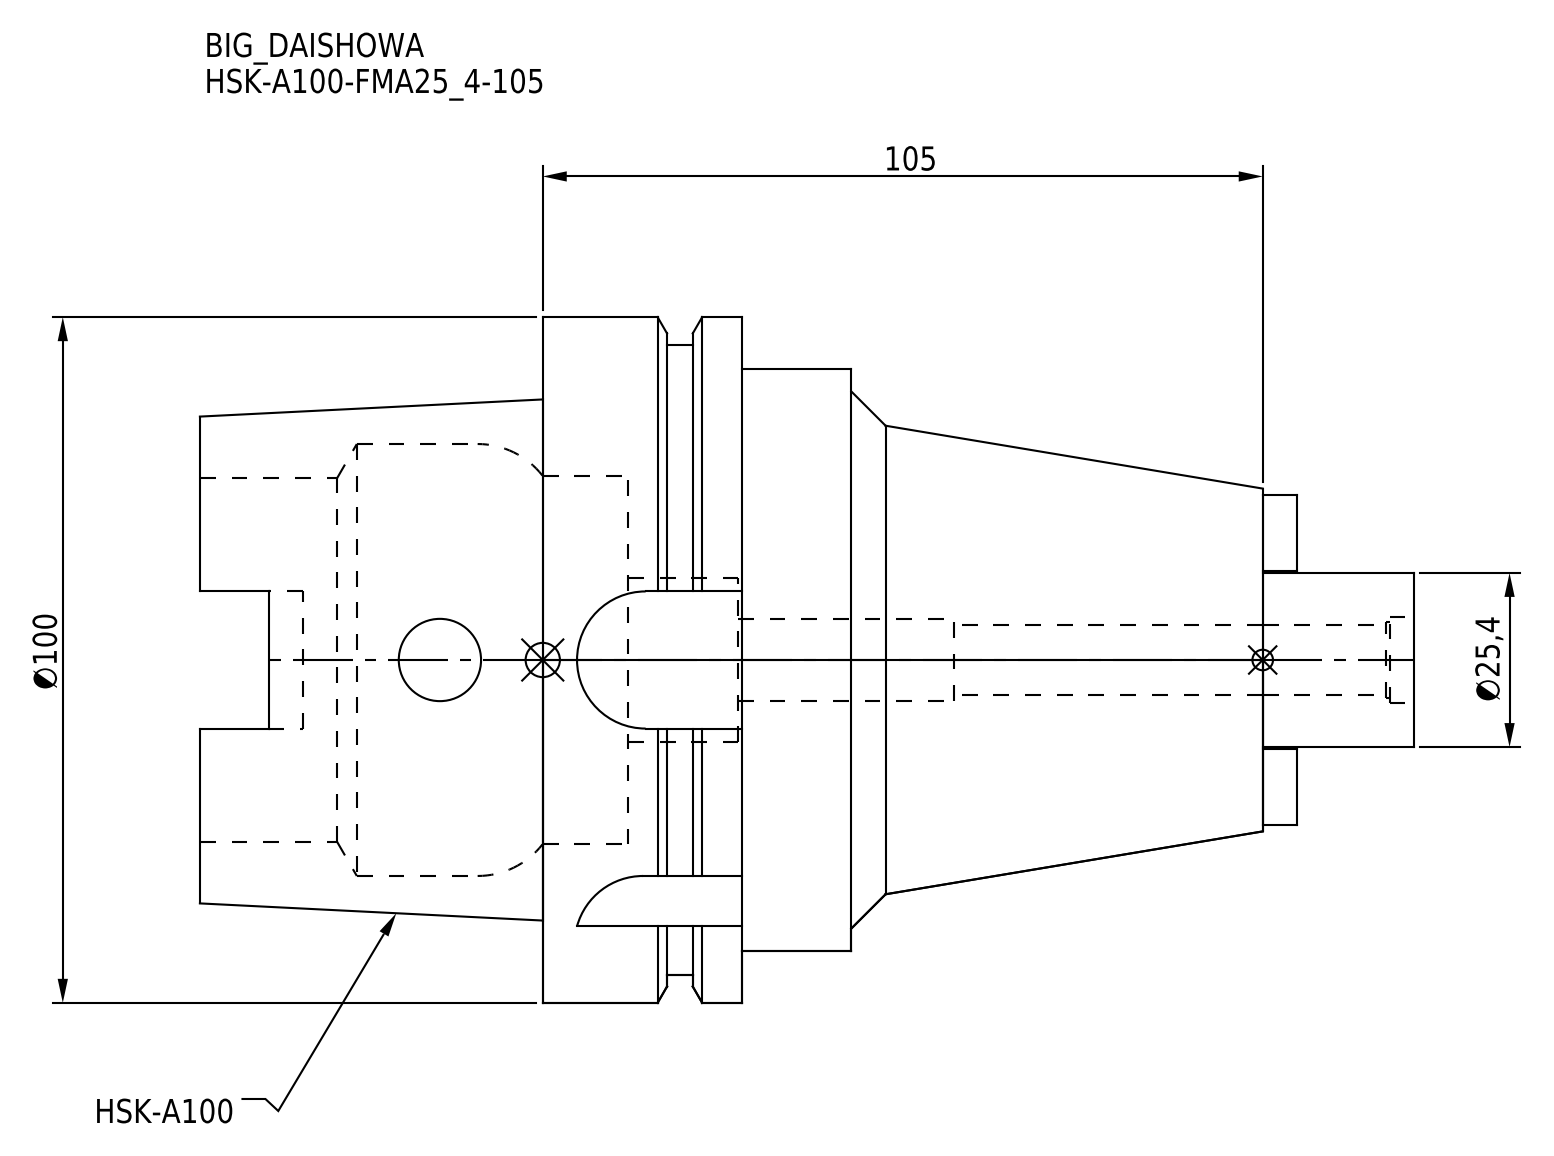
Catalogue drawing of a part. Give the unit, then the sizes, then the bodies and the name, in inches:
Units: inches
Overall size (bounding box): 6.969 × 3.937 × 3.937
Round holes (diameter × count): ⌀0.472 ×2, ⌀0.404 ×1, ⌀0.433 ×1, ⌀0.492 ×1, ⌀0.945 ×1, ⌀2.087 ×1, ⌀2.118 ×1, ⌀2.48 ×1
Round bosses / shafts (diameter × count): ⌀3.937 ×1, ⌀3.622 ×1, ⌀3.346 ×1, ⌀1 ×1
Partial cylindrical surfaces — rounded edges, fillets, slot ends (radius × count): R0.192 ×4, R0.394 ×4
Main face-to-face distances: 0.652, 1.142, 0.49, 4.134, 2.992, 3.644, 0.63, 1.969, 6.102, 3.11
Volume: 31.78 in³ · Surface area: 106.6 in²
Bodies: 1 solid, 109 faces (47 planar, 44 cylindrical, 18 other)
Part name (STEP PRODUCT): HSK-A100-FMA25_4-105
STEP written by: CREO PARAMETRIC BY PTC INC, 2016380 (AUTOMOTIVE_DESIGN)
